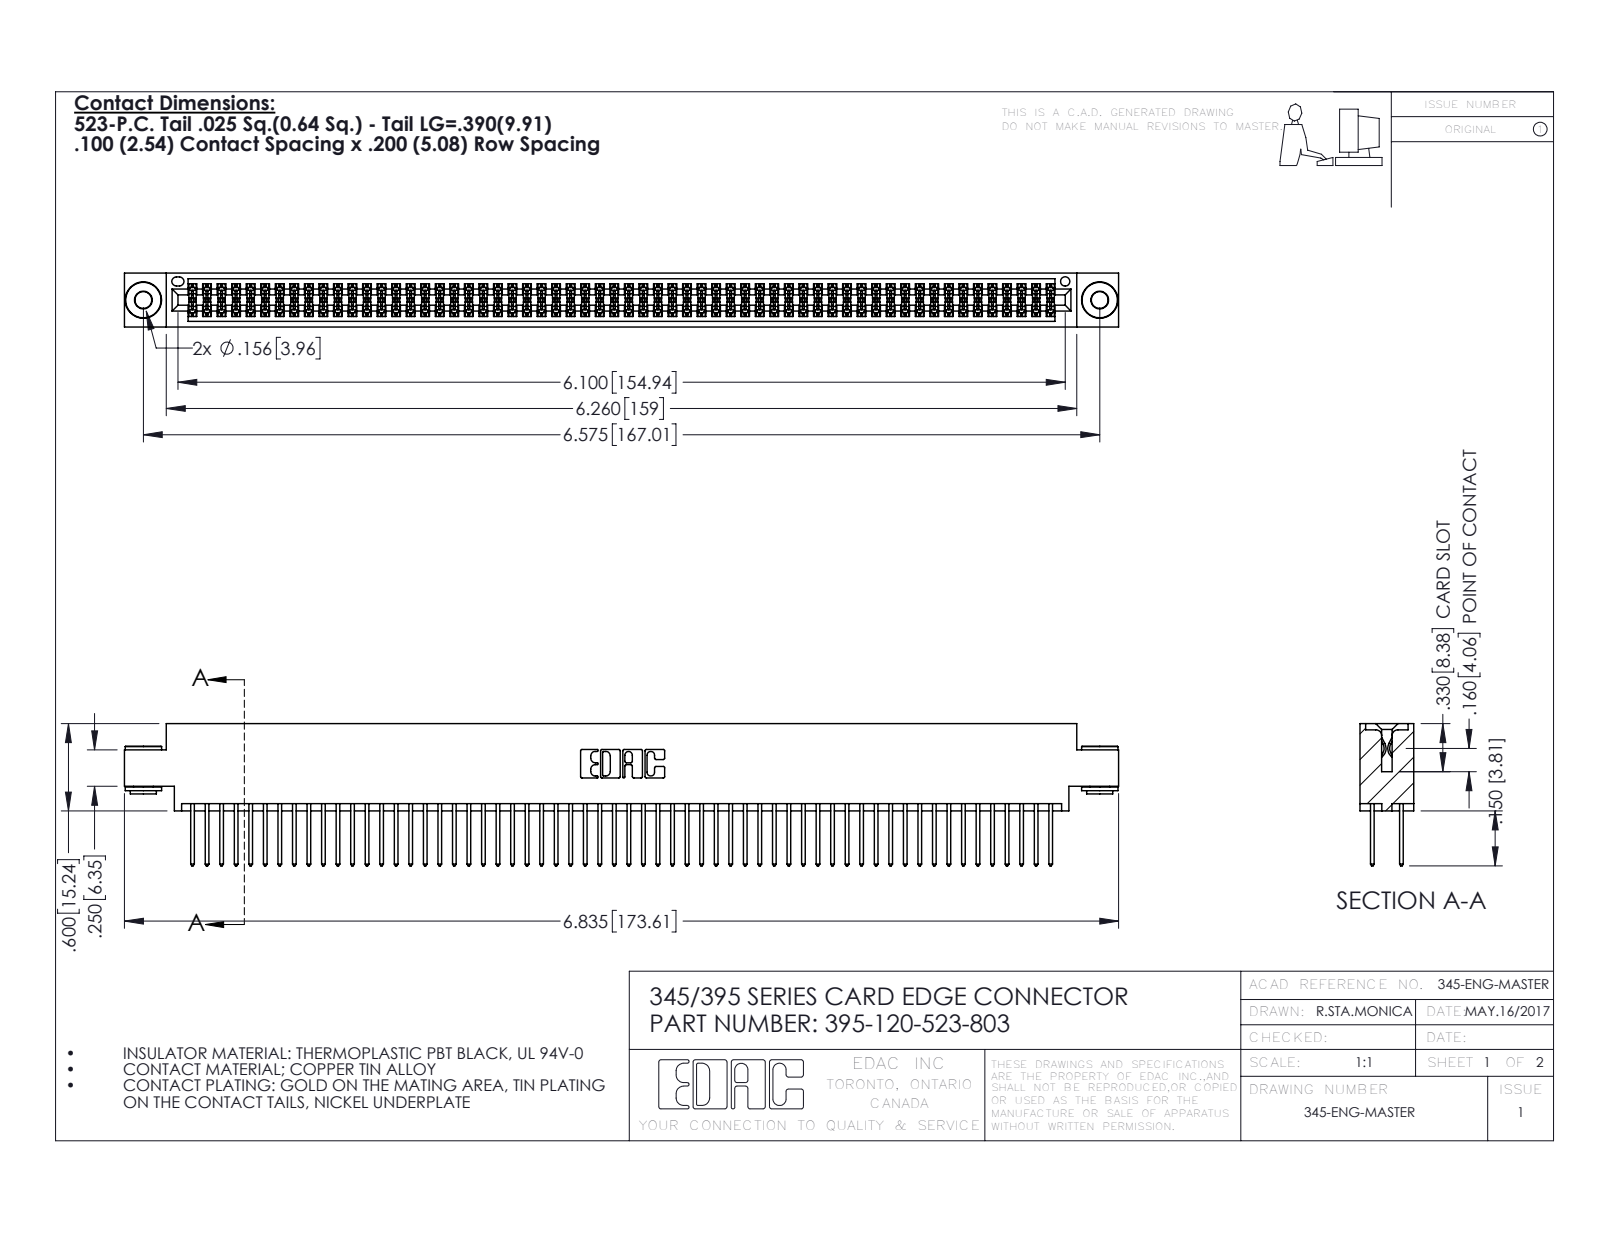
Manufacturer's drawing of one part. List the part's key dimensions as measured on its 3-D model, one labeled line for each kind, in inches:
Part name (STEP PRODUCT): 345-292-001_345-293-123; 345 Part_0.170 Offset - 0.156 Dia-TH; 345-250-002_345-250-002-102; 395-120-523-803
STEP written by: SolidWorks 2016 (CONFIG_CONTROL_DESIGN)
Units: inches
Bodies: 123 solids, 6168 faces (4054 planar, 2106 cylindrical, 8 other)
Overall size (bounding box): 6.835 × 0.977 × 0.37
Volume: 1.049 in³ · Surface area: 42.16 in²
Round holes (diameter × count): ⌀0.116 ×2, ⌀0.156 ×2, ⌀0.064 ×1
Round bosses / shafts (diameter × count): ⌀0.25 ×2, ⌀0.18 ×2, ⌀0.136 ×2
Partial cylindrical surfaces — rounded edges, fillets, slot ends (radius × count): R0.006 ×180, R0.01 ×120, R0.01 ×22, R0.007 ×6, R0.031 ×6, R0.026 ×3, R0.014 ×2, R0.019 ×2
Main face-to-face distances: 0.072, 0.298, 0.2, 0.098, 0.272, 0.025, 0.37, 0.225, 0.175, 0.149
Hole centre spacings: 0.27, 6.339, 6.575
